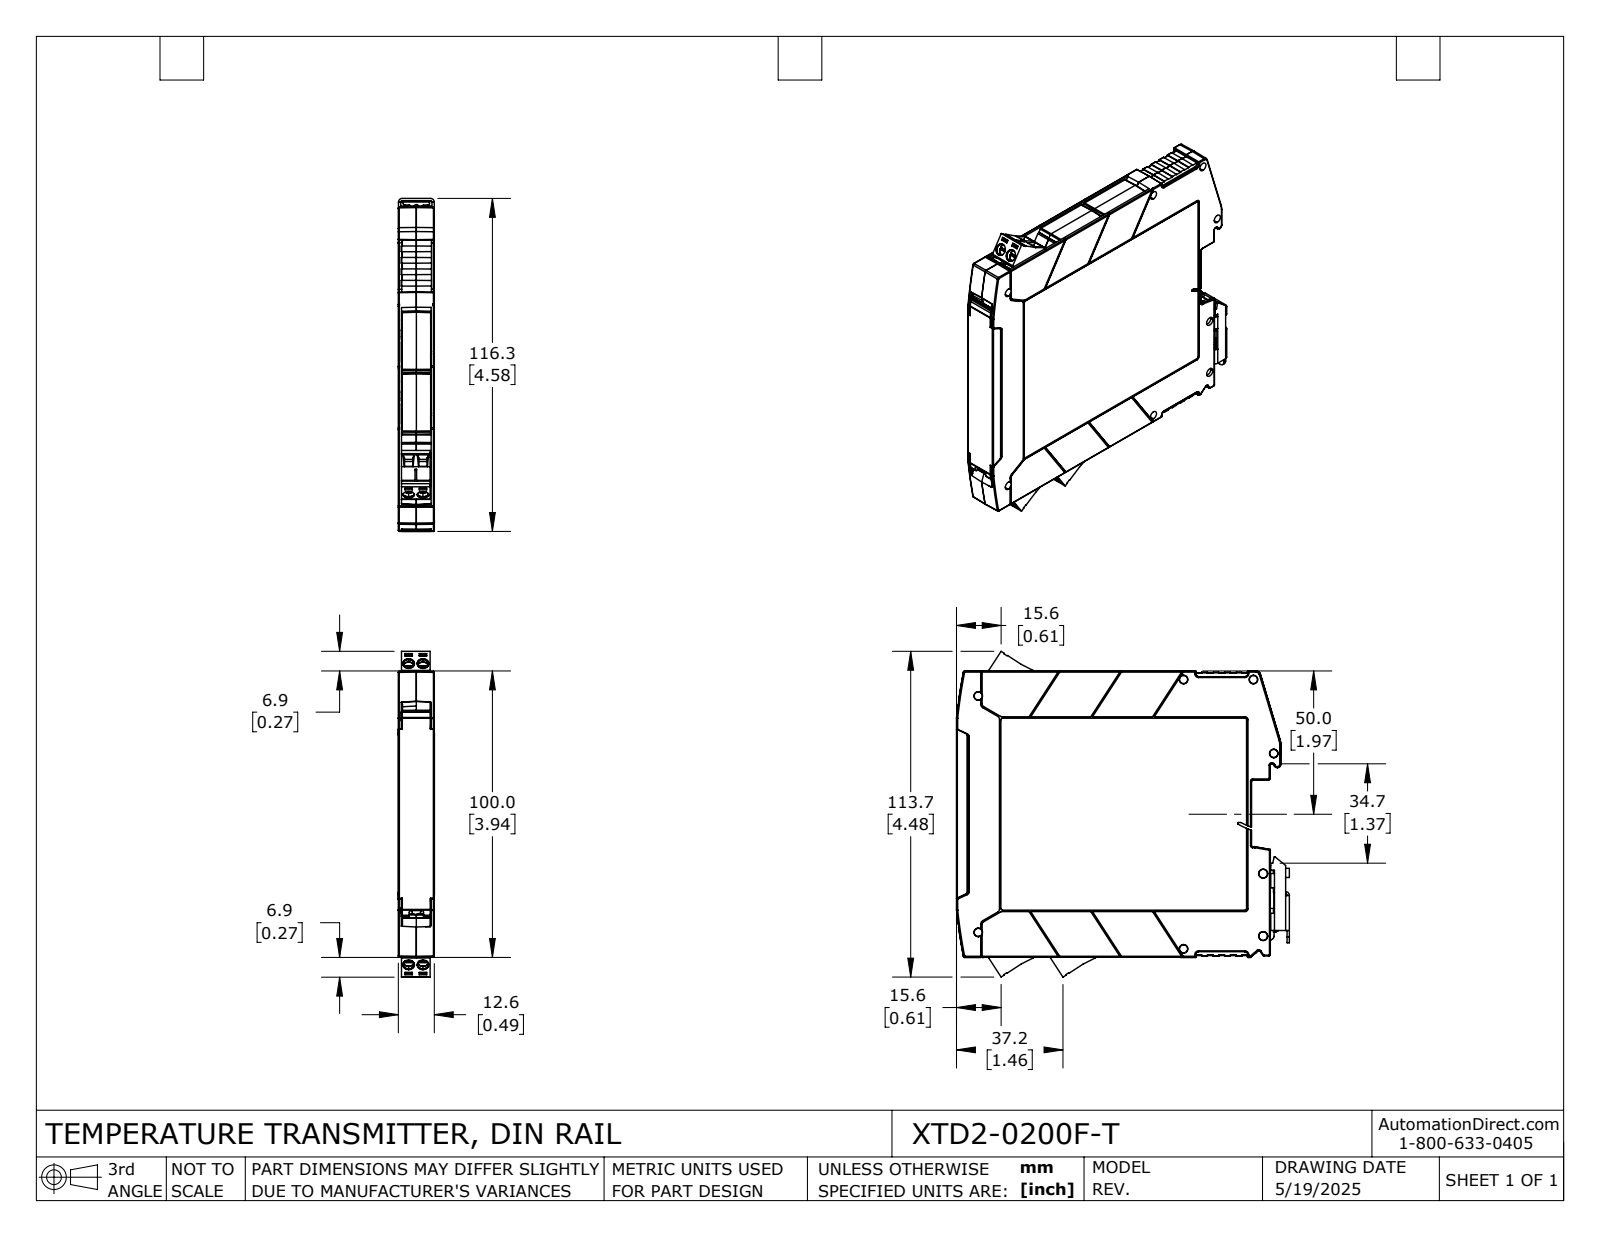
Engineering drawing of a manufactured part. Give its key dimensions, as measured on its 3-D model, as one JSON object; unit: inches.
{"part_name": "XTD2-0200F-T", "step_written_by": "SolidWorks 2024 (AUTOMOTIVE_DESIGN)", "units": "inches", "bodies": {"solids": 14, "faces": 3337, "planar": 1910, "cylindrical": 596, "other": 831}, "overall_size": [4.577, 4.478, 0.496], "volume_in3": 2.41, "surface_area_in2": 101.5, "round_holes": [[0.063, 6], [0.11, 6], [0.152, 6], [0.159, 6]], "round_bosses_or_shafts": [[0.156, 6], [0.098, 6], [0.059, 2], [0.053, 2]], "partial_cylinders_radius": [[0.008, 89], [0.012, 78], [0.02, 71], [0.039, 22], [0.004, 20], [0.016, 13], [0.006, 12], [0.028, 8]], "face_to_face_distances": [0.049, 0.445, 0.494, 0.396, 0.043, 0.451, 0.402, 0.031, 0.198, 0.247], "hole_center_spacings": [0.197, 0.464, 0.504, 0.713, 0.739]}
